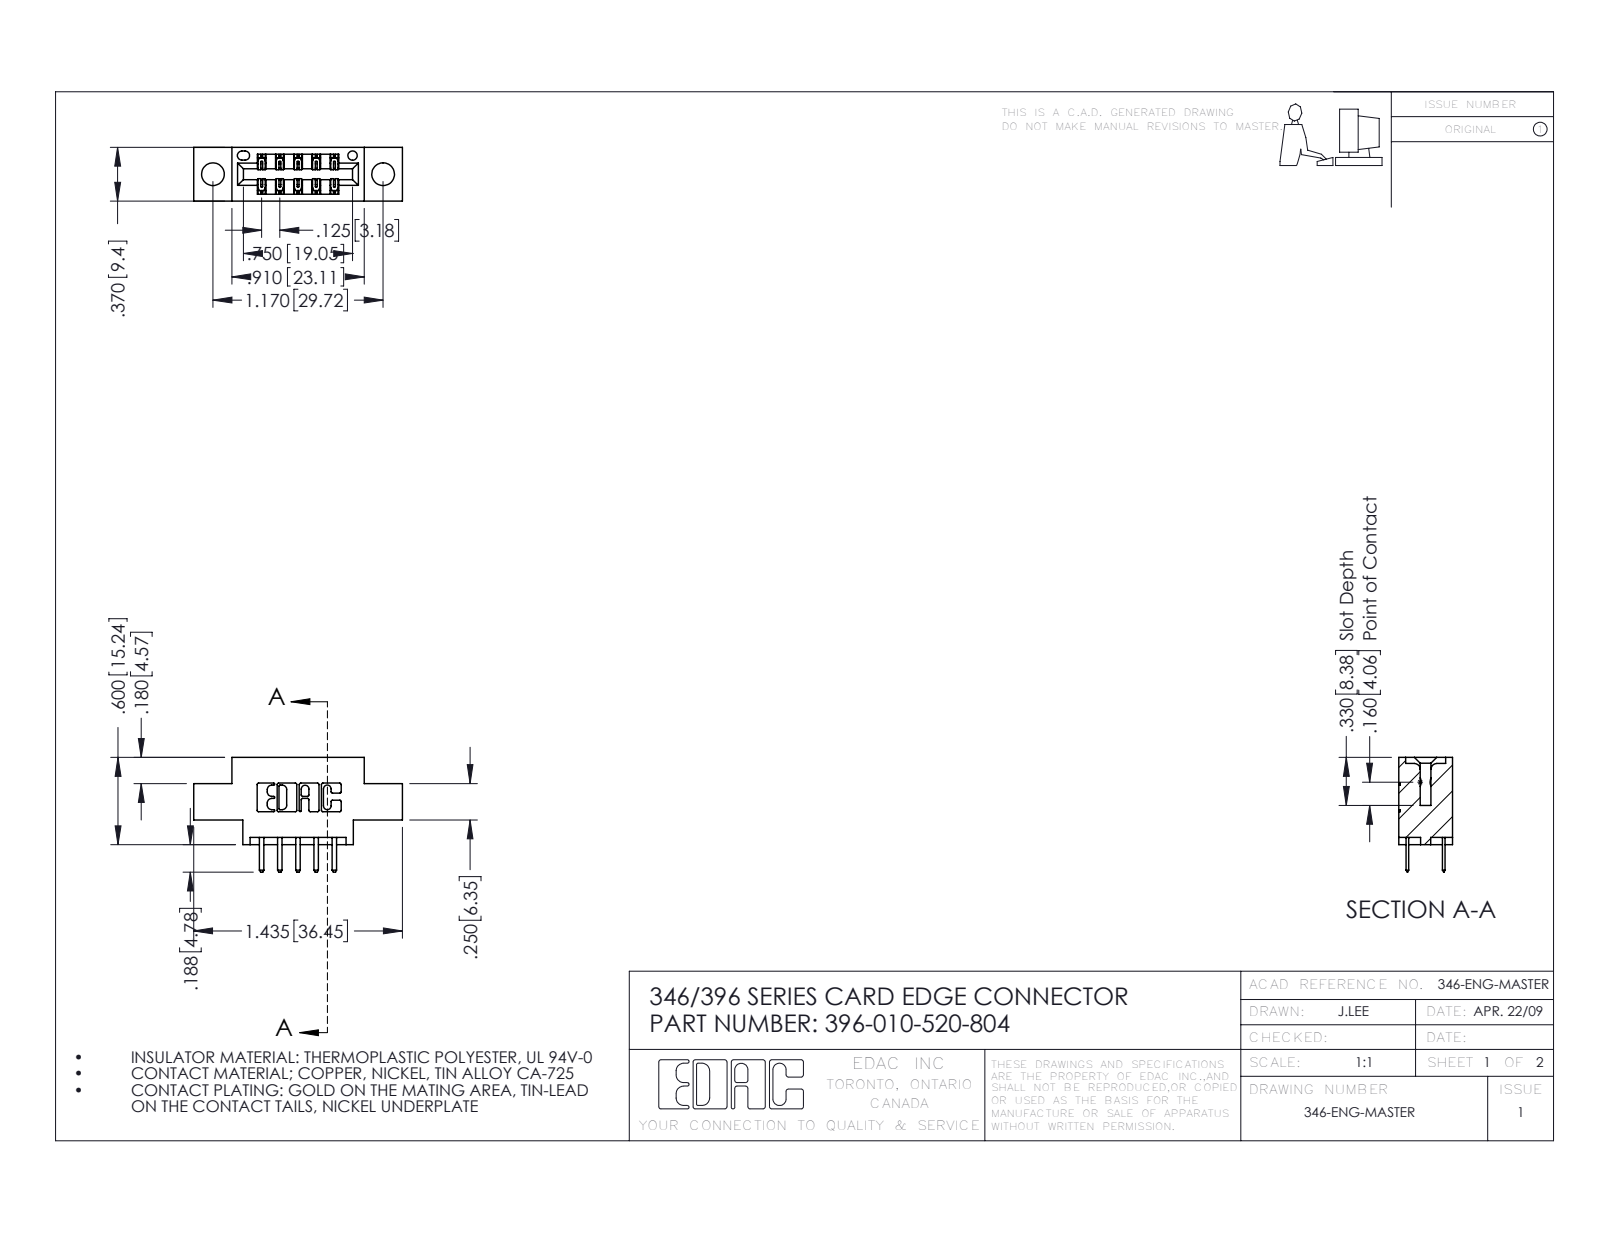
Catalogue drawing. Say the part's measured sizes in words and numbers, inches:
The part is named "346 Part_0.170 Offset - 0.156 Dia-TH; 345-292-001_345-293-120; 396-010-520-804". Its 3-D file was written by "SolidWorks 2016 (CONFIG_CONTROL_DESIGN)". It is 11 solids with 686 faces: 450 planar, 236 cylindrical and 0 other. Overall it measures 1.435 by 0.788 by 0.37 inches. Its volume is 0.184 cubic inches and its surface area 5.506 square inches. Round holes: 2 of diameter 0.156, 1 of diameter 0.064. Partial cylindrical surfaces (rounded edges, fillets, slot ends): 22 of radius 0.01, 15 of radius 0.006, 14 of radius 0.01, 6 of radius 0.007, 6 of radius 0.031, 3 of radius 0.026, 2 of radius 0.014, 2 of radius 0.022. The main face-to-face distances are 0.25, 0.37, 0.048, 0.322, 0.148, 0.222, 0.1, 0.174, 0.55, 0.072. The hole center spacings are 0.246, 0.969, 1.17.
